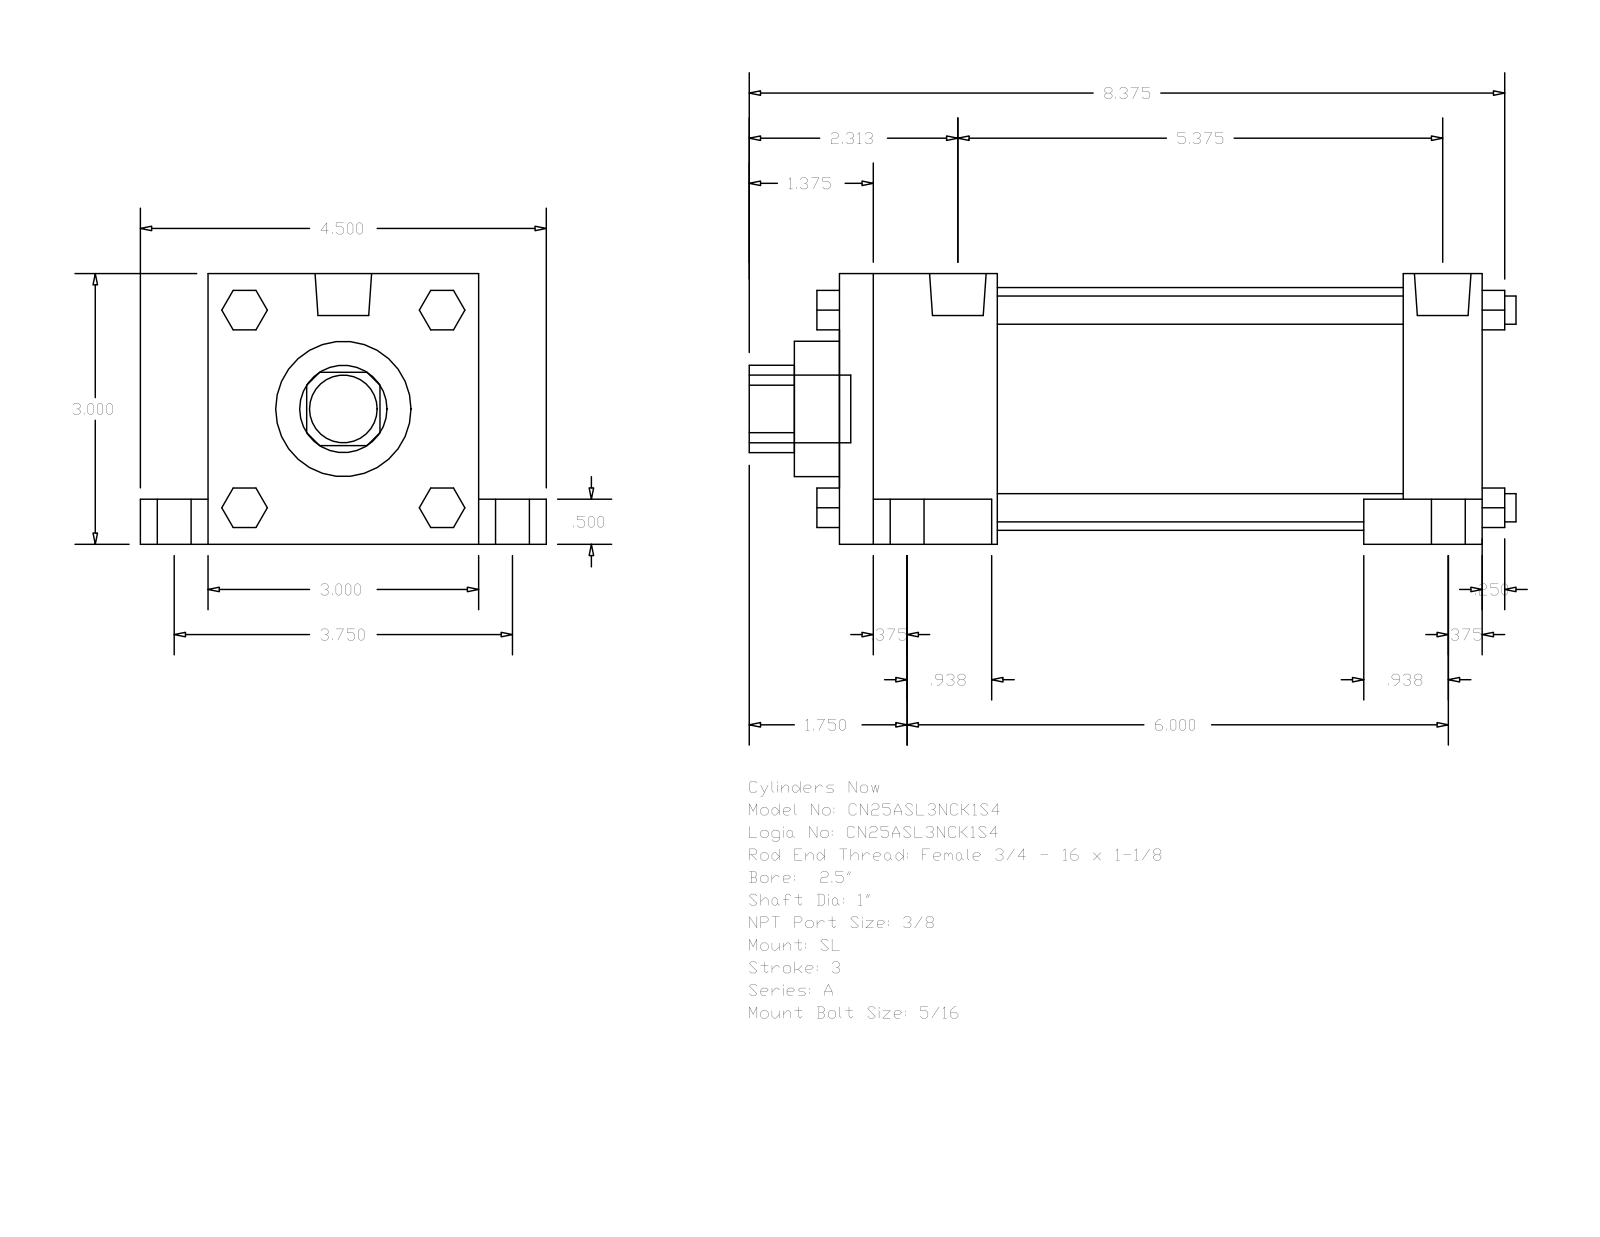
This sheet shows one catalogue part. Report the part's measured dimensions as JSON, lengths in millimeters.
{"part_name": "A_SL__0250_1", "step_written_by": "GSSL Pune (CONFIG_CONTROL_DESIGN)", "units": "millimeters", "bodies": {"solids": 0, "faces": 148, "planar": 112, "cylindrical": 36, "other": 0}, "overall_size": [215.9, 114.3, 76.2], "round_holes": [[25.4, 1], [38.1, 1], [68.33, 1]], "round_bosses_or_shafts": [[15.88, 4], [9.53, 4], [7.94, 4], [5.56, 4], [15.93, 2], [19.05, 1]], "partial_cylinders_radius": [[12.29, 1]], "face_to_face_distances": [76.2, 180.98, 114.3, 12.7, 44.45, 136.53, 158.75, 22.23, 19.05, 63.5]}
